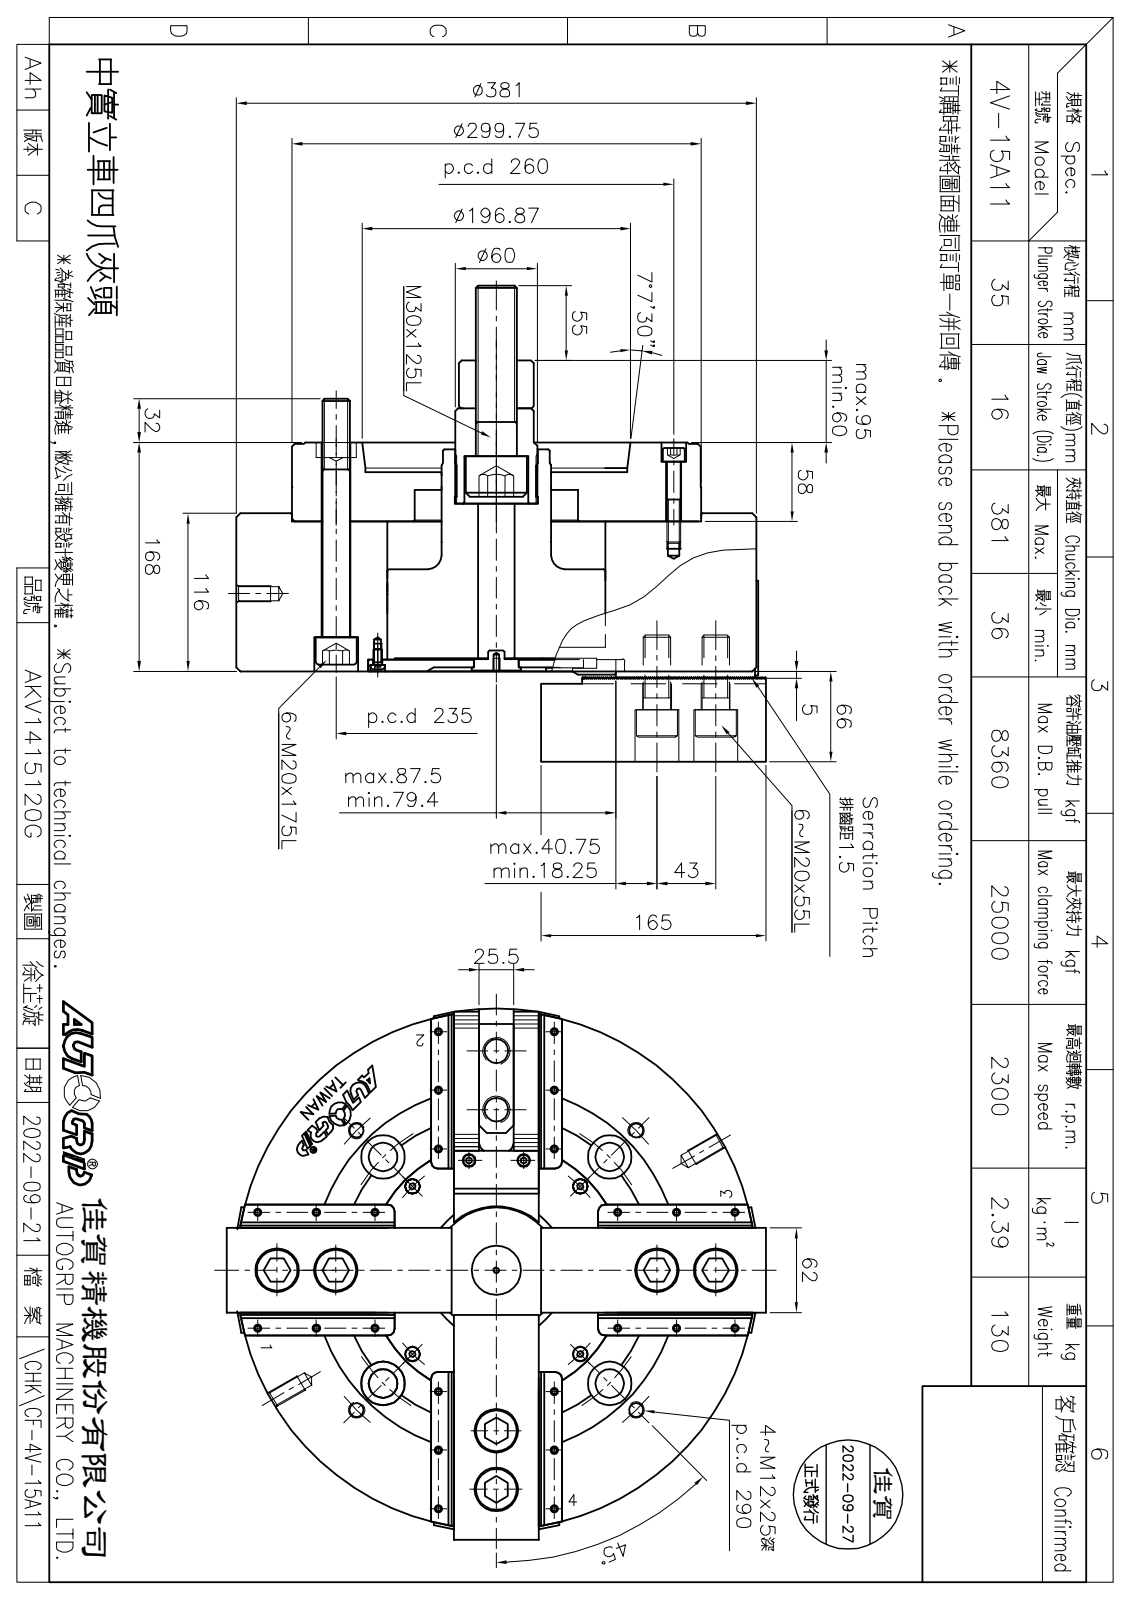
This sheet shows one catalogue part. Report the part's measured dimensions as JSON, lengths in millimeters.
{"part_name": "圓頭內六角螺栓_M10x60; CF-3V-15-05010; 圓頭內六角螺栓_M20x120; CF-4V-15-06000 (+8 more)", "step_written_by": "SolidWorks 2016 (CONFIG_CONTROL_DESIGN)", "units": "millimeters", "bodies": {"solids": 93, "faces": 8713, "planar": 6146, "cylindrical": 2084, "other": 483}, "overall_size": [416.5, 416.5, 349.2], "volume_mm3": 17790000, "surface_area_mm2": 1672000, "round_holes": [[5.5, 32], [5, 25], [4.2, 24], [21, 20], [32, 12], [11, 10], [9.5, 8], [20, 8], [18, 6], [6, 4], [6.6, 4], [10.2, 4]], "round_bosses_or_shafts": [[9.5, 24], [30, 12], [5, 11], [8.5, 8], [20, 4], [10.5, 4], [16, 3], [10, 3]], "partial_cylinders_radius": [[0.1, 720], [2, 8], [5, 8], [13.25, 4], [13.5, 4], [190.5, 4], [76, 1]], "face_to_face_distances": [110, 8.5, 62, 6, 58, 101.5, 52, 1, 116, 107.5], "hole_center_spacings": [43, 95.26, 85, 146.21, 169.1, 186.64, 33.42, 41.02]}
